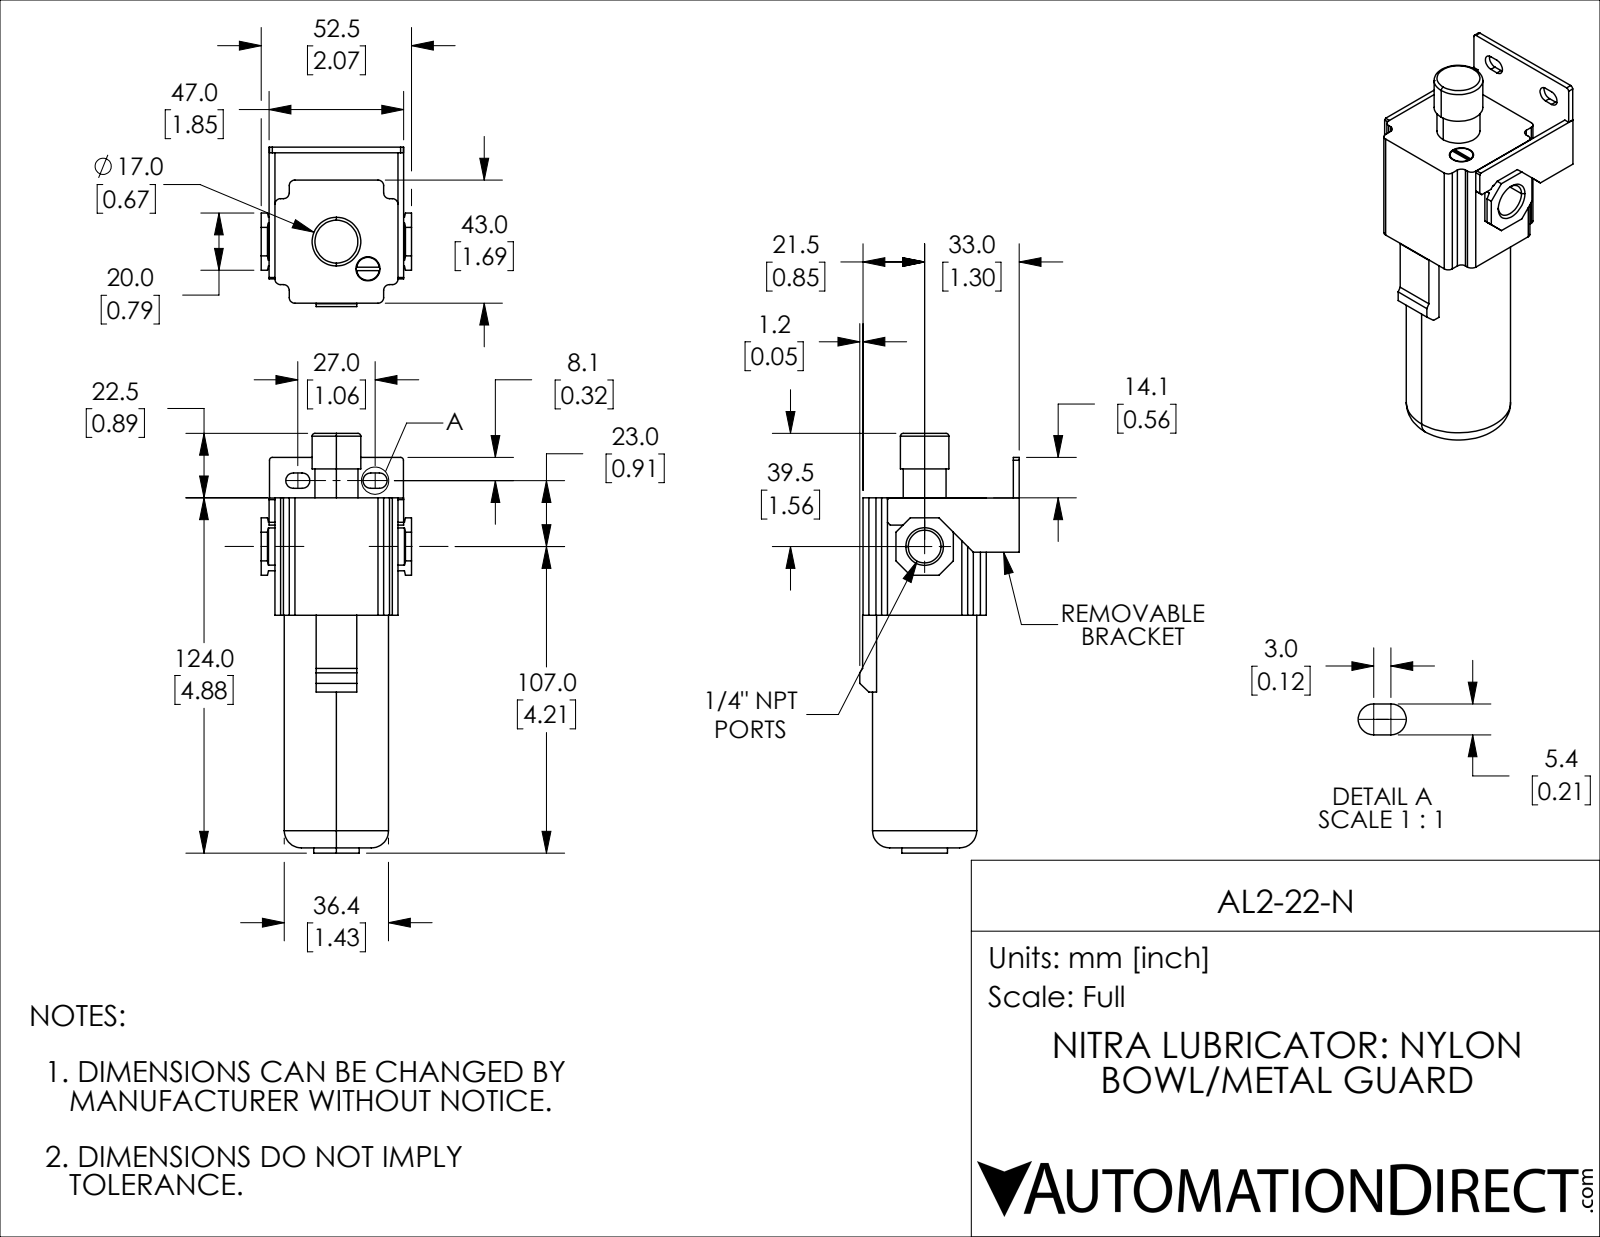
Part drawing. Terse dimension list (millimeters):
name: AL2-22-N
written by: SolidWorks 2019 (CONFIG_CONTROL_DESIGN)
unit: mm
bodies: 1 solid, 137 faces (95 planar, 34 cylindrical, 8 other)
size: 146.5 × 55.67 × 52.5
volume: 166 008 mm³; area: 27 290 mm²
holes: 1× ⌀8.4, 1× ⌀11.45
bosses: 1× ⌀36.4, 1× ⌀17, 1× ⌀15.9, 1× ⌀15, 1× ⌀8
rounds: 12× R2, 4× R2.7, 2× R1
face distances: 2, 43, 52.5, 11.5, 45, 9.5, 54.5, 41, 47, 5
